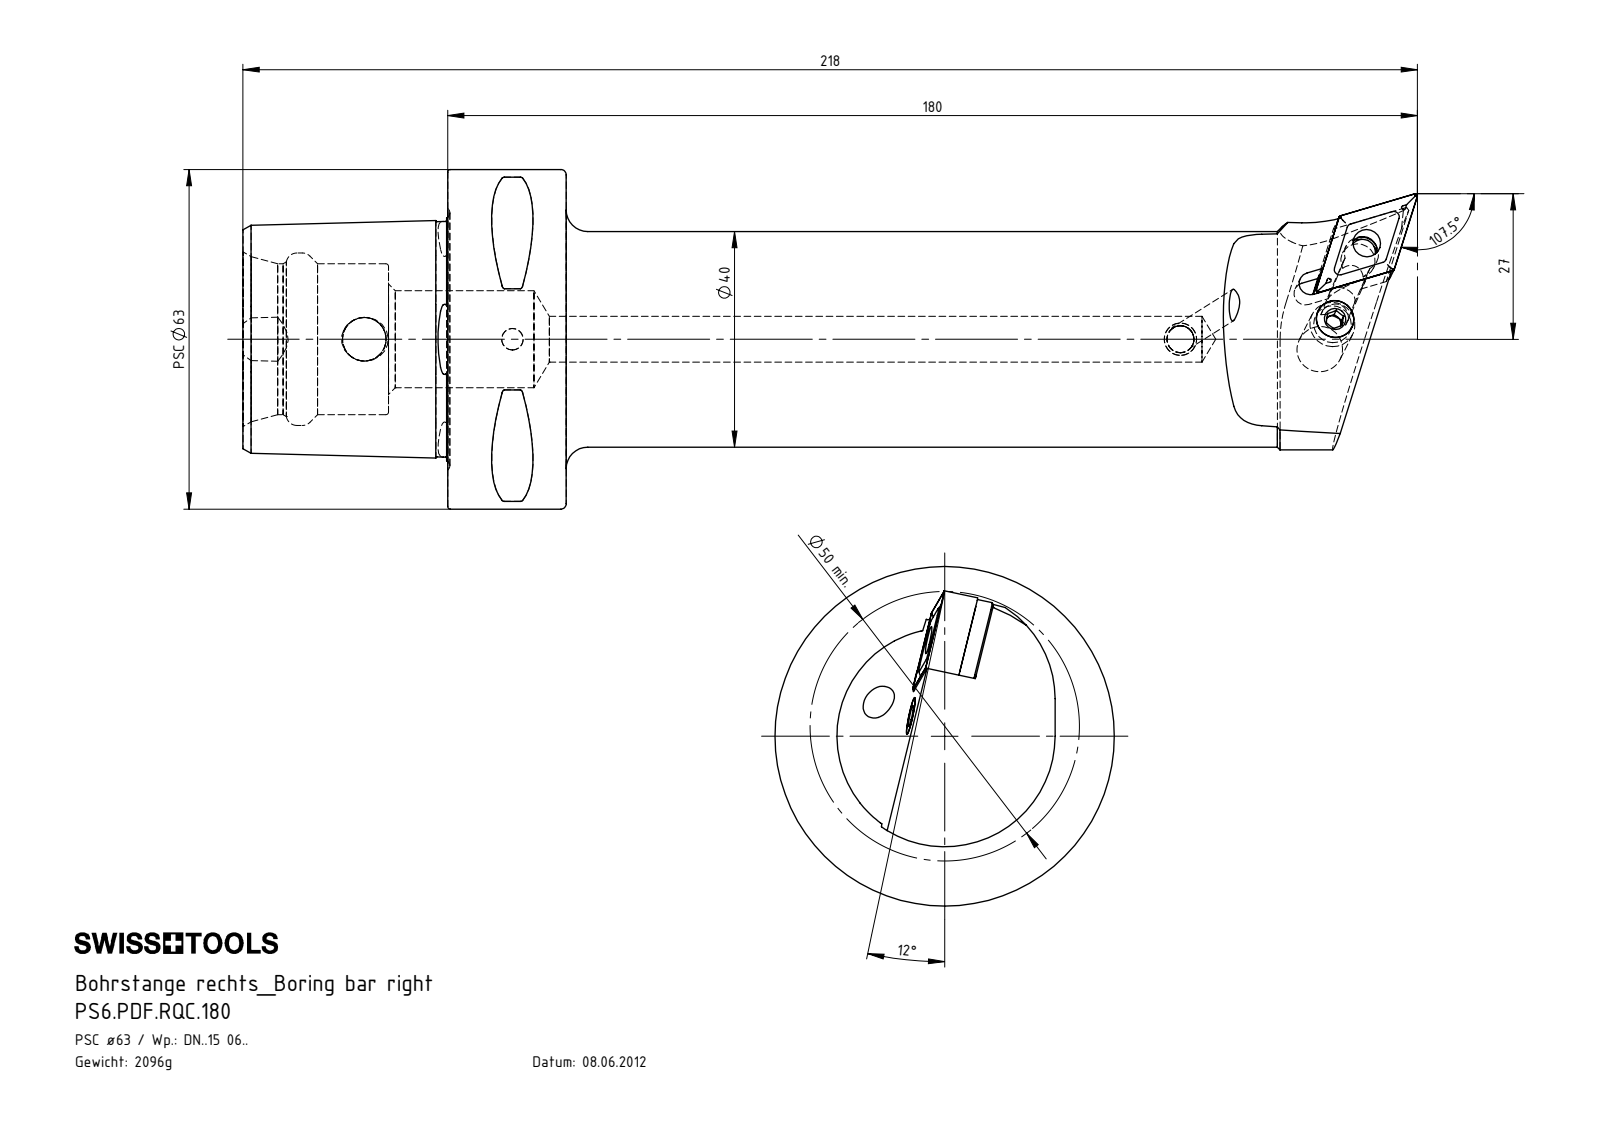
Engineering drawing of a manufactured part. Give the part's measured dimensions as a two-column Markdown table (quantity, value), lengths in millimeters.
| quantity | value |
| --- | --- |
| part name | WDF-ER2.101.003_A; WDF-ER3.101.000_A; KVT_MB_600_060; PS6.PDF.RQC.180 (+4 more) |
| STEP written by | SolidWorks 2017 (AUTOMOTIVE_DESIGN) |
| units | millimeters |
| bodies | 8 solids, 346 faces (92 planar, 87 cylindrical, 167 other) |
| overall size | 218 × 63 × 63 |
| volume | 267 824 mm³ |
| surface area | 46 097 mm² |
| round holes (diameter × count) | 5 × 2, 4 × 1, 5.16 × 1, 6.4 × 1, 7 × 1, 8.1 × 1, 8.4 × 1, 8.5 × 1, 18 × 1, 28 × 1, 32 × 1 |
| round bosses / shafts (diameter × count) | 63 × 1, 40 × 1, 8 × 1, 7.9 × 1, 6.4 × 1, 6 × 1, 4.7 × 1, 3.55 × 1 |
| partial cylindrical surfaces (radius × count) | 0.5 × 8, 0.4 × 4, 1 × 4, 2.5 × 2, 2.1 × 1, 2.35 × 1, 2.8 × 1, 3 × 1 |
| main face-to-face distances | 22, 38, 60, 6.05, 12.27, 24.88, 3.18, 9.23, 27, 11 |
| hole center spacings | 15.6, 27.5, 124, 151.5 |
